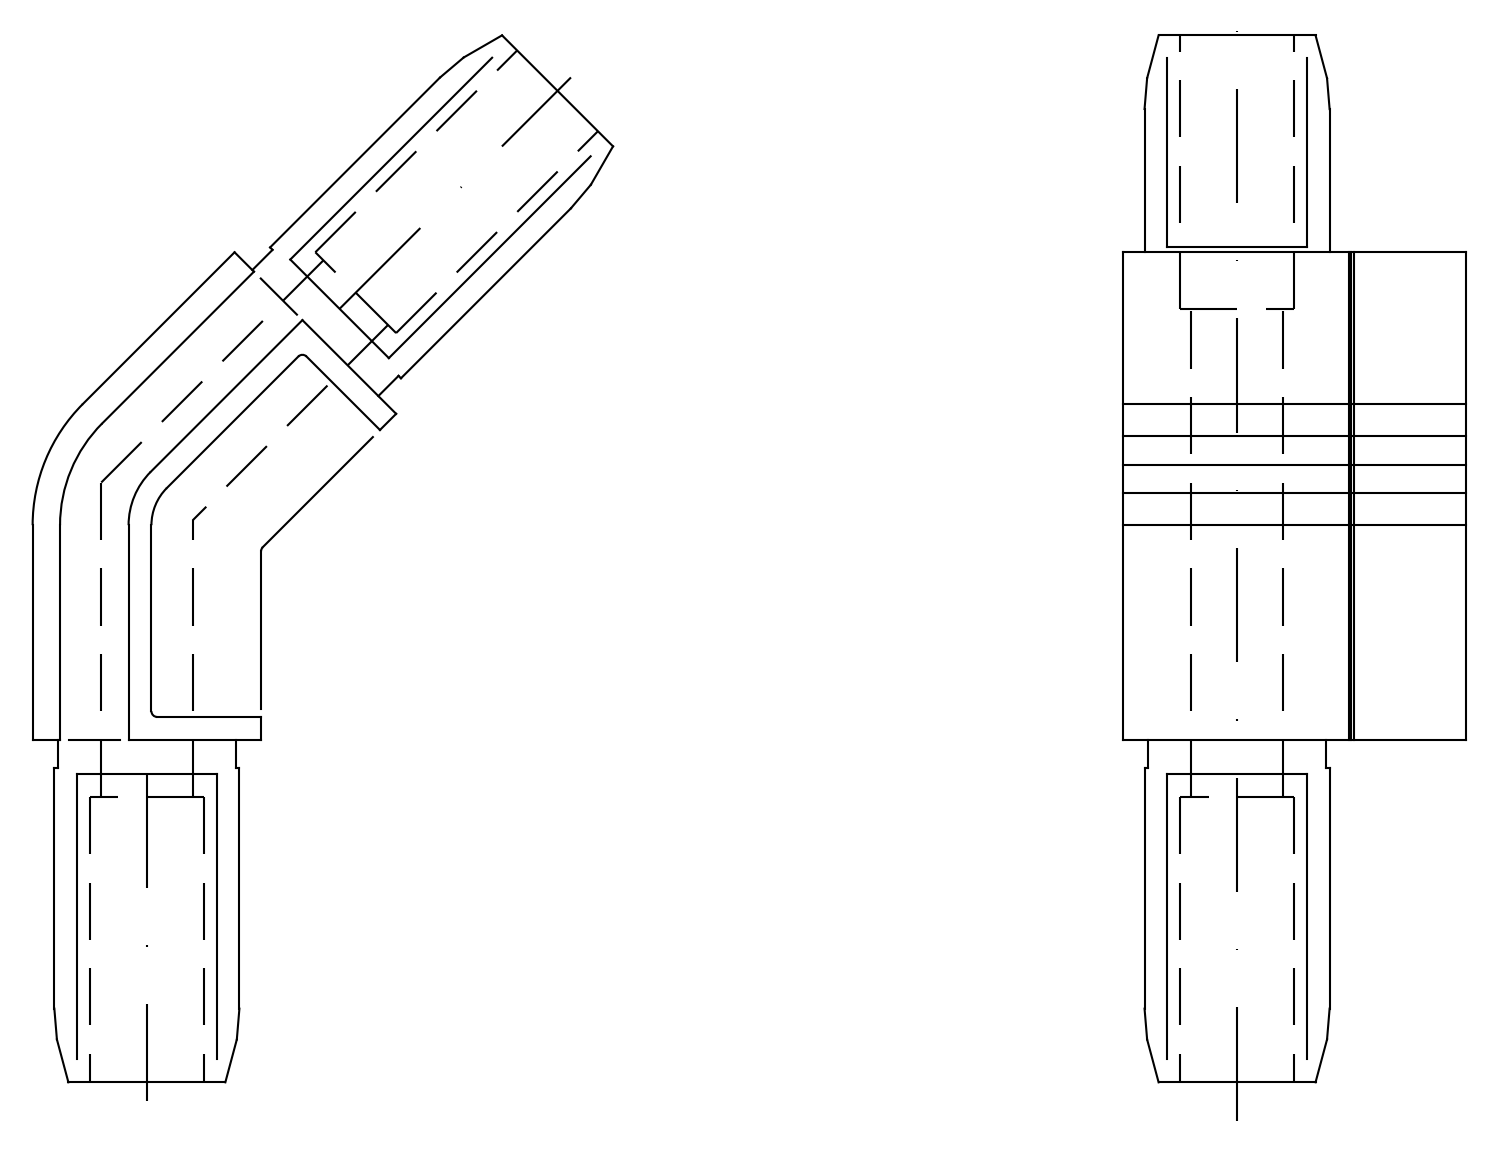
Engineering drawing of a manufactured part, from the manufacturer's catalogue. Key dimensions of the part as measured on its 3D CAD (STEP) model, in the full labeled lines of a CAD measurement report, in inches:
STEP written by: THINKDESIGN (CONFIG_CONTROL_DESIGN)
Units: inches
Bodies: 1 solid, 132 faces (75 planar, 43 cylindrical, 14 other)
Overall size (bounding box): 3.608 × 2 × 1.181
Volume: 1.884 in³ · Surface area: 17.52 in²
Round holes (diameter × count): ⌀0.315 ×2
Partial cylindrical surfaces — rounded edges, fillets, slot ends (radius × count): R0.039 ×22, R0.079 ×10, R0.02 ×3, R0.354 ×2, R0.181 ×1, R0.26 ×1, R0.496 ×1, R0.591 ×1
Main face-to-face distances: 0.075, 0.713, 0.638, 0.787, 0.087, 0.712, 0.079, 0.701, 0.626, 0.457
